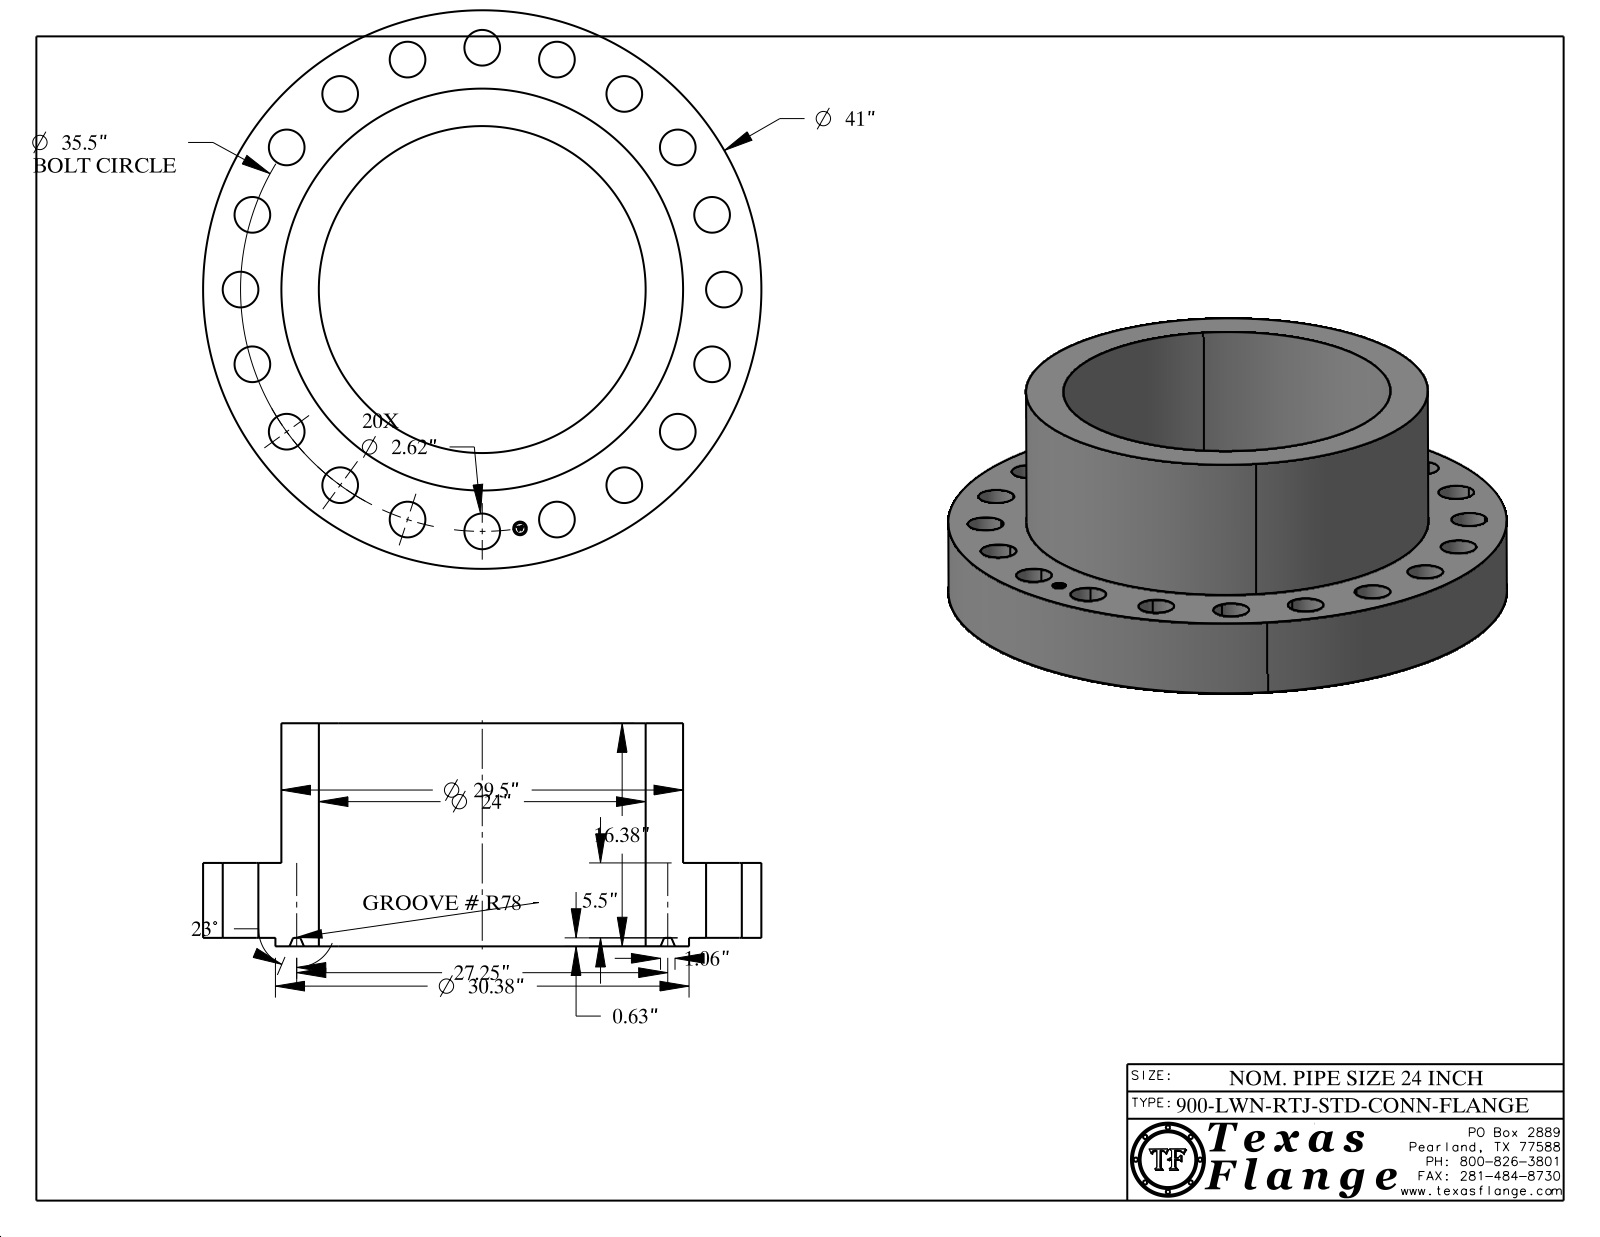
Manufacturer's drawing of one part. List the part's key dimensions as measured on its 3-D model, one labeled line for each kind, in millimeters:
Part name (STEP PRODUCT): 24-900-LWN-RTJ-STD-CONN-FLANGE
STEP written by: CATIA V5 STEP AP214 (AUTOMOTIVE_DESIGN)
Units: millimetres
Bodies: 1 solid, 447 faces (371 planar, 68 cylindrical, 8 other)
Overall size (bounding box): 1041.4 × 1041.4 × 415.9
Volume: 109 400 000 mm³ · Surface area: 3 514 000 mm²
Round holes (diameter × count): ⌀66.5 ×20, ⌀25.4 ×1, ⌀609.6 ×1
Round bosses / shafts (diameter × count): ⌀1.5 ×8, ⌀1041.4 ×1, ⌀771.5 ×1, ⌀749.3 ×1, ⌀20 ×1
Main face-to-face distances: 139.7, 400.1, 260.4, 15.9, 155.6, 415.9, 155.4, 139.6, 260.5, 7.6
Hole centre spacings: 450.9, 278.6, 729.5, 803.4, 409.4, 530, 637.6, 857.6
